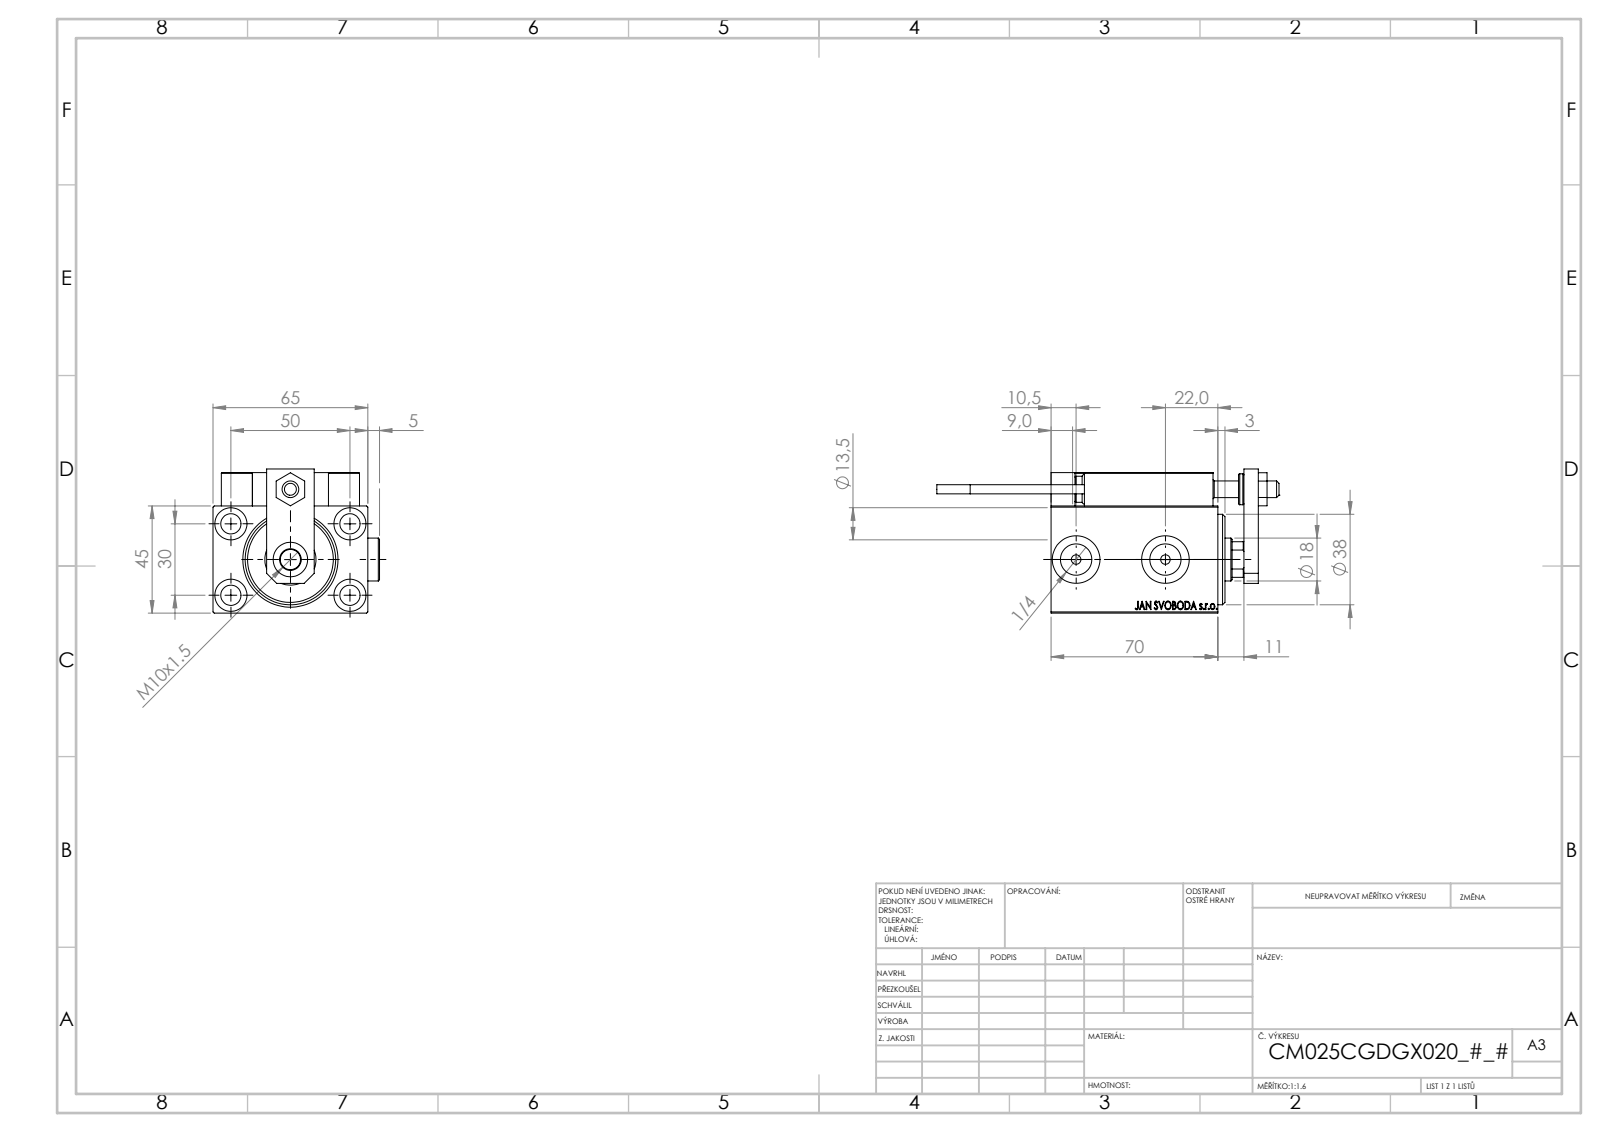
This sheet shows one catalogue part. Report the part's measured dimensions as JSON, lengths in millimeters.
{"part_name": "SWITCH X; ZARAZKA; SWITCH_X_FRONT_BACK; ALLEN BOLT D8 (+8 more)", "step_written_by": "SolidWorks 2019 (CONFIG_CONTROL_DESIGN)", "units": "millimeters", "bodies": {"solids": 25, "faces": 1336, "planar": 594, "cylindrical": 204, "other": 538}, "overall_size": [143.7, 69.9, 60.5], "volume_mm3": 221635, "surface_area_mm2": 72075, "round_holes": [[4, 6], [8, 5], [8.5, 5], [3.2, 4], [13.5, 4], [5, 2], [13.16, 2], [20, 2], [7, 1], [14.5, 1], [18, 1], [21.5, 1]], "round_bosses_or_shafts": [[18, 2], [5, 2], [3.8, 2], [13, 1], [11, 1]], "partial_cylinders_radius": [[0.3, 30], [3, 2], [8.5, 1]], "face_to_face_distances": [45, 59, 14, 65, 6, 5, 3, 19, 13, 7], "hole_center_spacings": [29.15, 11.37, 20, 22.09, 28.9, 29.59, 29.69, 30]}
